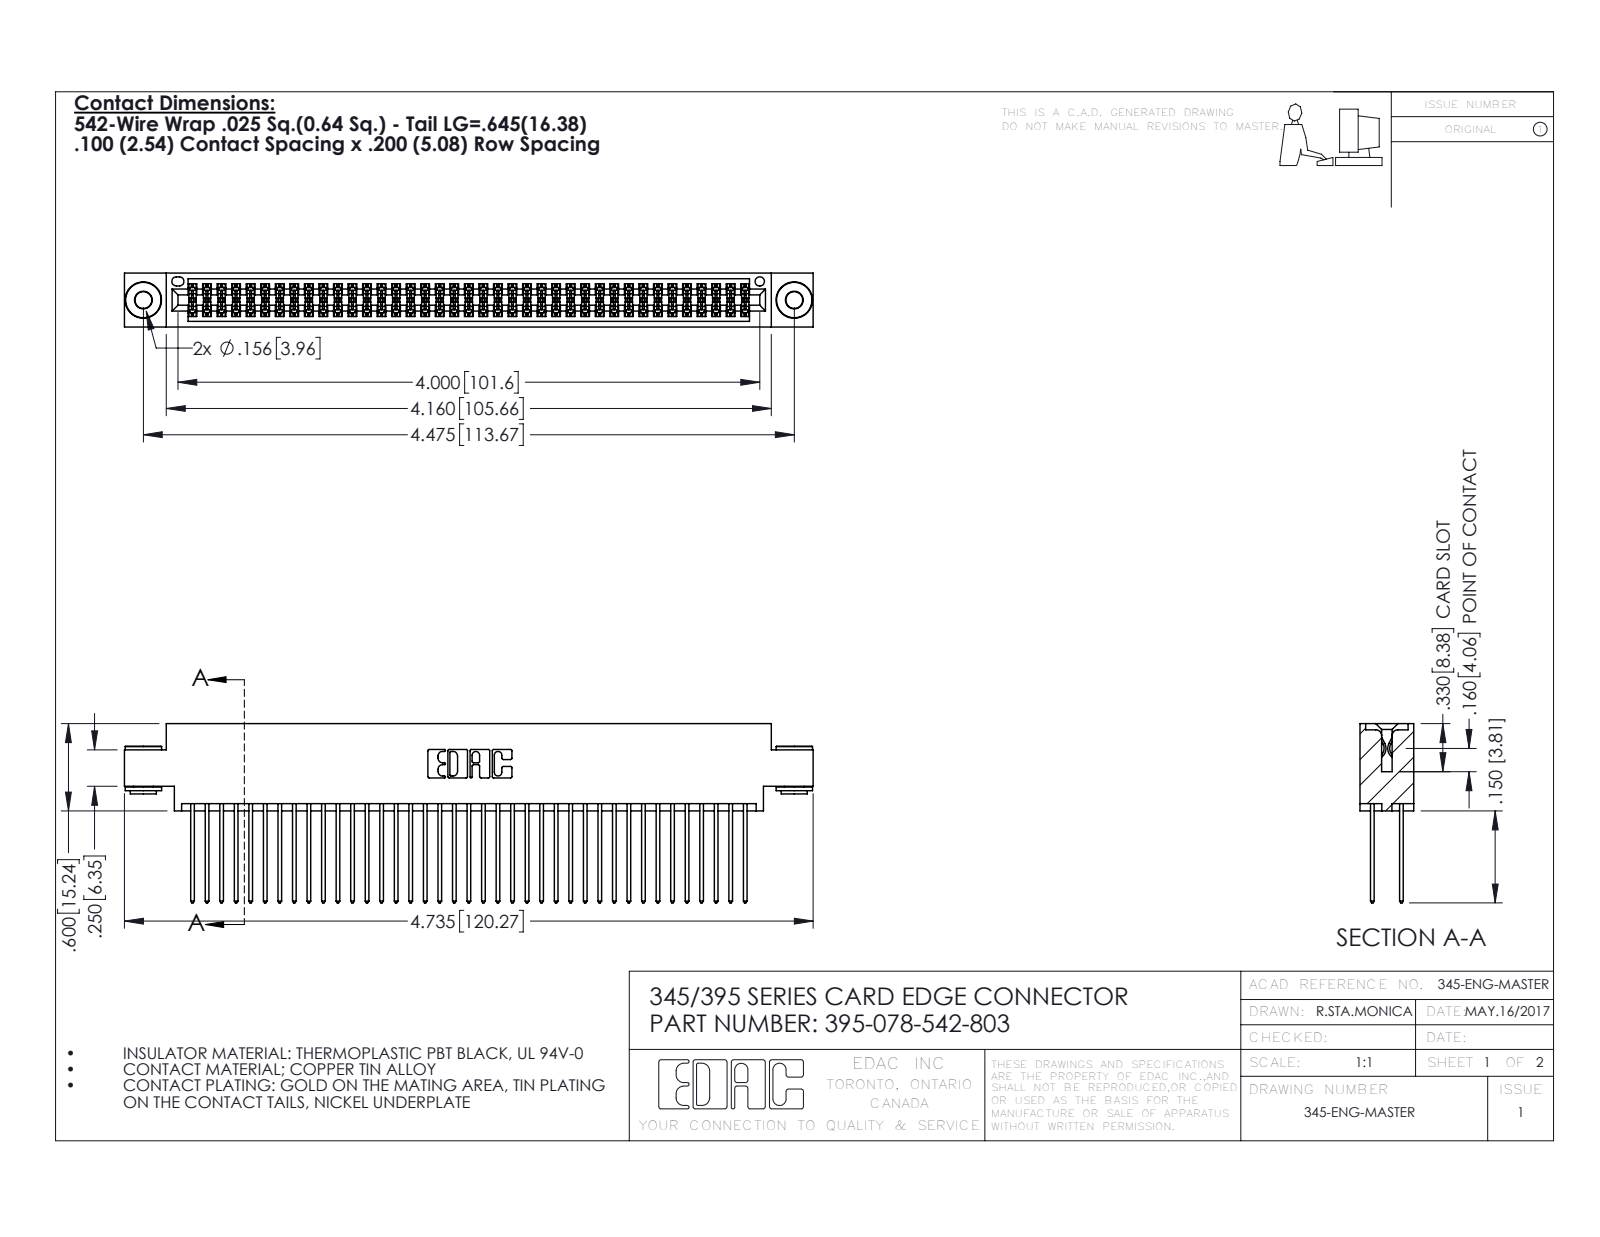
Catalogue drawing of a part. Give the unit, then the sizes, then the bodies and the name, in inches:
Units: inches
Overall size (bounding box): 4.735 × 1.232 × 0.37
Round holes (diameter × count): ⌀0.116 ×2, ⌀0.156 ×2, ⌀0.064 ×1
Round bosses / shafts (diameter × count): ⌀0.25 ×2, ⌀0.18 ×2, ⌀0.136 ×2
Partial cylindrical surfaces — rounded edges, fillets, slot ends (radius × count): R0.006 ×117, R0.01 ×78, R0.01 ×22, R0.007 ×6, R0.031 ×6, R0.026 ×3, R0.014 ×2, R0.019 ×2
Main face-to-face distances: 0.072, 0.298, 0.2, 0.098, 0.272, 0.025, 0.37, 0.225, 0.175, 0.149
Hole centre spacings: 0.27, 4.239, 4.475
Volume: 0.728 in³ · Surface area: 30.41 in²
Bodies: 81 solids, 4068 faces (2668 planar, 1392 cylindrical, 8 other)
Part name (STEP PRODUCT): 345-292-001_345-293-142; 345-250-002_345-250-002-102; 345 Part_0.170 Offset - 0.156 Dia-TH; 395-078-542-803
STEP written by: SolidWorks 2016 (CONFIG_CONTROL_DESIGN)
